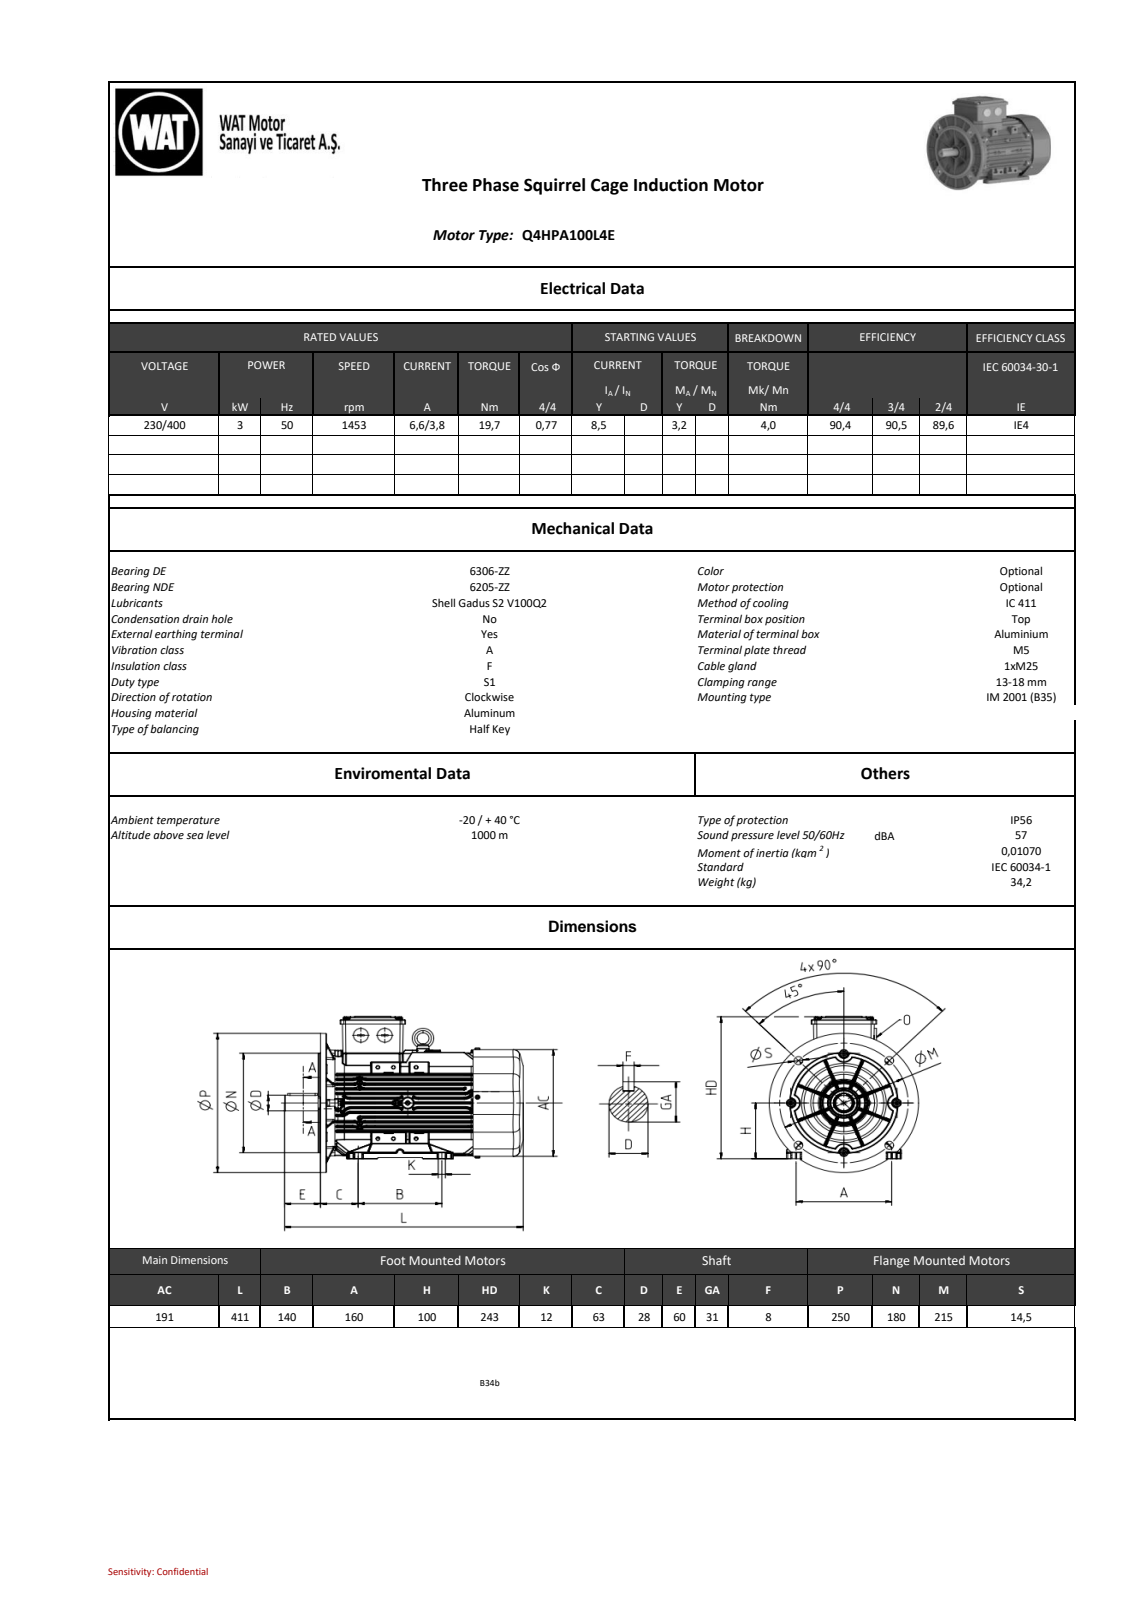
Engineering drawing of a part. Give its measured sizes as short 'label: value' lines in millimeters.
name: QH100 B3 KTA-M2_stp_objects
written by: SIEMENS PLM Software NX2206.8101 (AUTOMOTIVE_DESIGN)
unit: mm
bodies: 0 solids, 6167 faces (1388 planar, 2226 cylindrical, 2553 other)
size: 411.25 × 267.54 × 249.94
holes: 4× ⌀6.5, 1× ⌀4, 1× ⌀10, 1× ⌀10.5, 1× ⌀12, 1× ⌀43.9, 1× ⌀44.1, 1× ⌀49.1, 1× ⌀52, 1× ⌀57.4, 1× ⌀78, 1× ⌀89
bosses: 8× ⌀8, 4× ⌀12, 4× ⌀8.28, 4× ⌀6, 1× ⌀180.5, 1× ⌀113.5, 1× ⌀93.5, 1× ⌀61
rounds: 569× R1, 551× R0.8, 122× R2, 85× R1.5, 53× R0.81, 41× R0.5, 36× R5, 26× R15
face distances: 8.53, 8.46, 8.45, 76.24, 16.91, 93.45, 25.58, 17.05, 76.68, 59.63
hole spacings: 64, 66.95, 105.32, 128, 143.11
